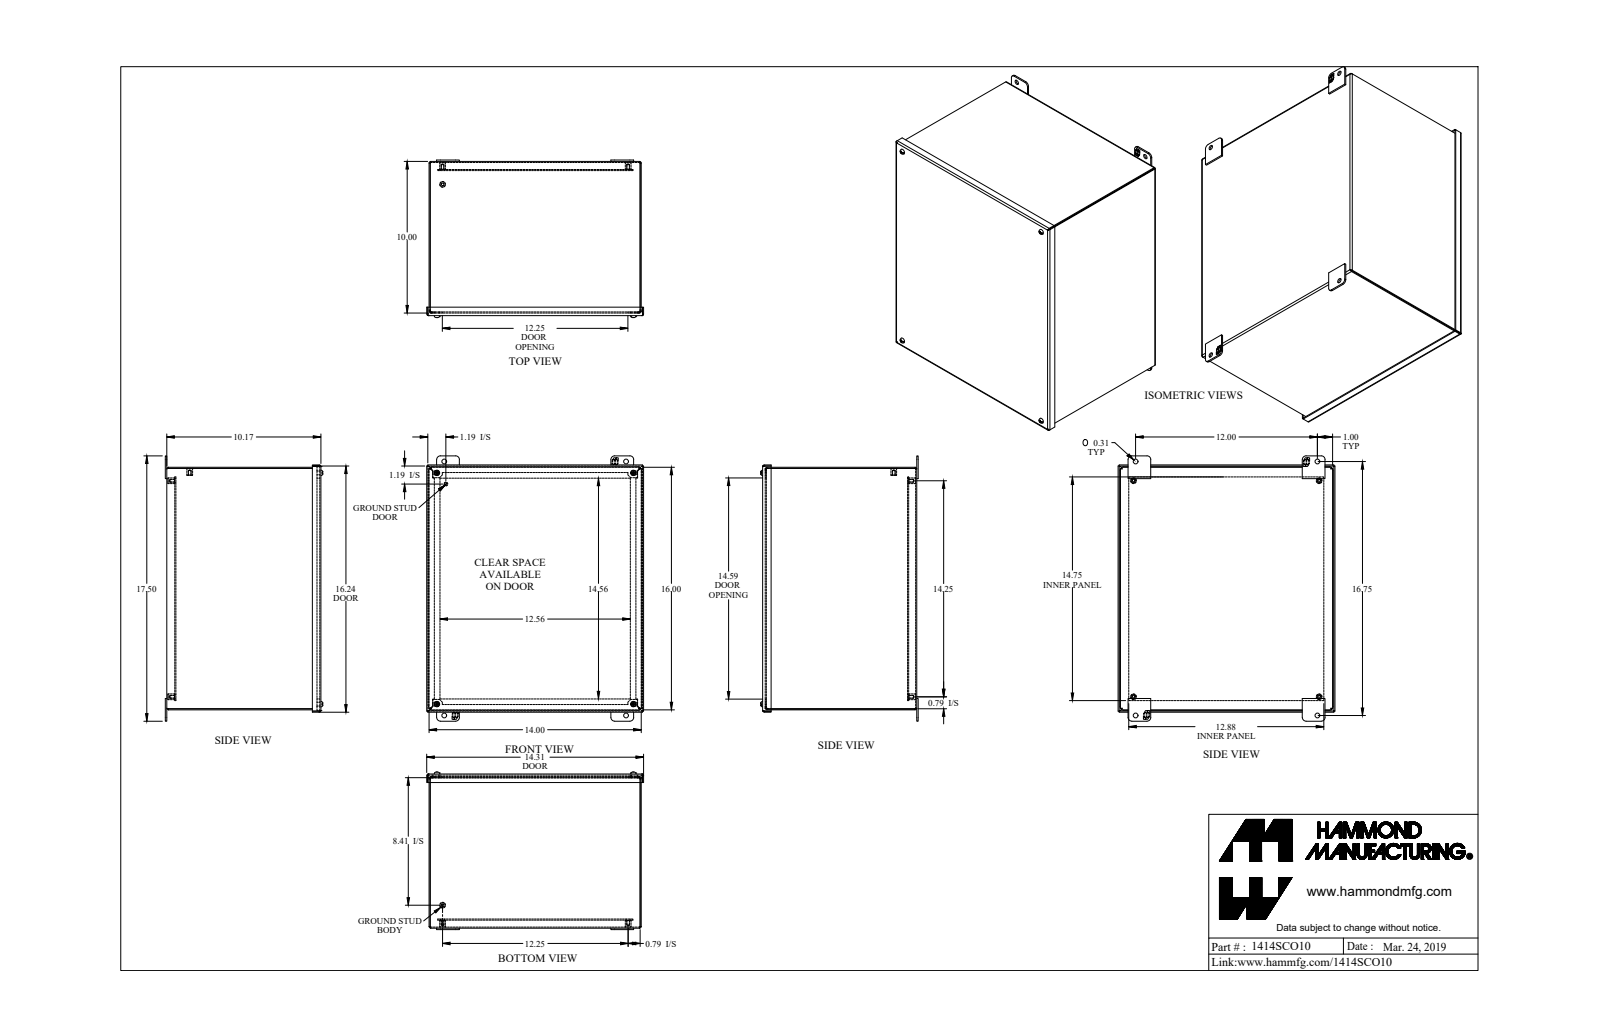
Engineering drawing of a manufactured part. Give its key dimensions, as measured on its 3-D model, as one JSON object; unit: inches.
{"part_name": "1414SCO10", "step_written_by": "SolidWorks 2019 (AUTOMOTIVE_DESIGN)", "units": "inches", "bodies": {"solids": 30, "faces": 710, "planar": 478, "cylindrical": 172, "other": 60}, "overall_size": [17.5, 14.312, 10.394], "volume_in3": 101.3, "surface_area_in2": 2718, "round_holes": [[0.156, 5], [0.159, 4], [0.25, 4], [0.265, 4], [0.312, 4]], "round_bosses_or_shafts": [[0.375, 5], [0.39, 4], [0.275, 4], [0.19, 4], [0.148, 4], [0.25, 1], [0.188, 1]], "partial_cylinders_radius": [[0.25, 12], [0.007, 8], [0.036, 8], [0.079, 8], [0.108, 8], [0.125, 8], [0.281, 8], [0.16, 4]], "face_to_face_distances": [0.072, 10.1, 9.568, 0.532, 13.928, 15.928, 10.172, 10.028, 9.64, 0.46], "hole_center_spacings": [12.502, 0.889, 16.008, 20.292, 12, 12.25, 12.956, 12.956]}
